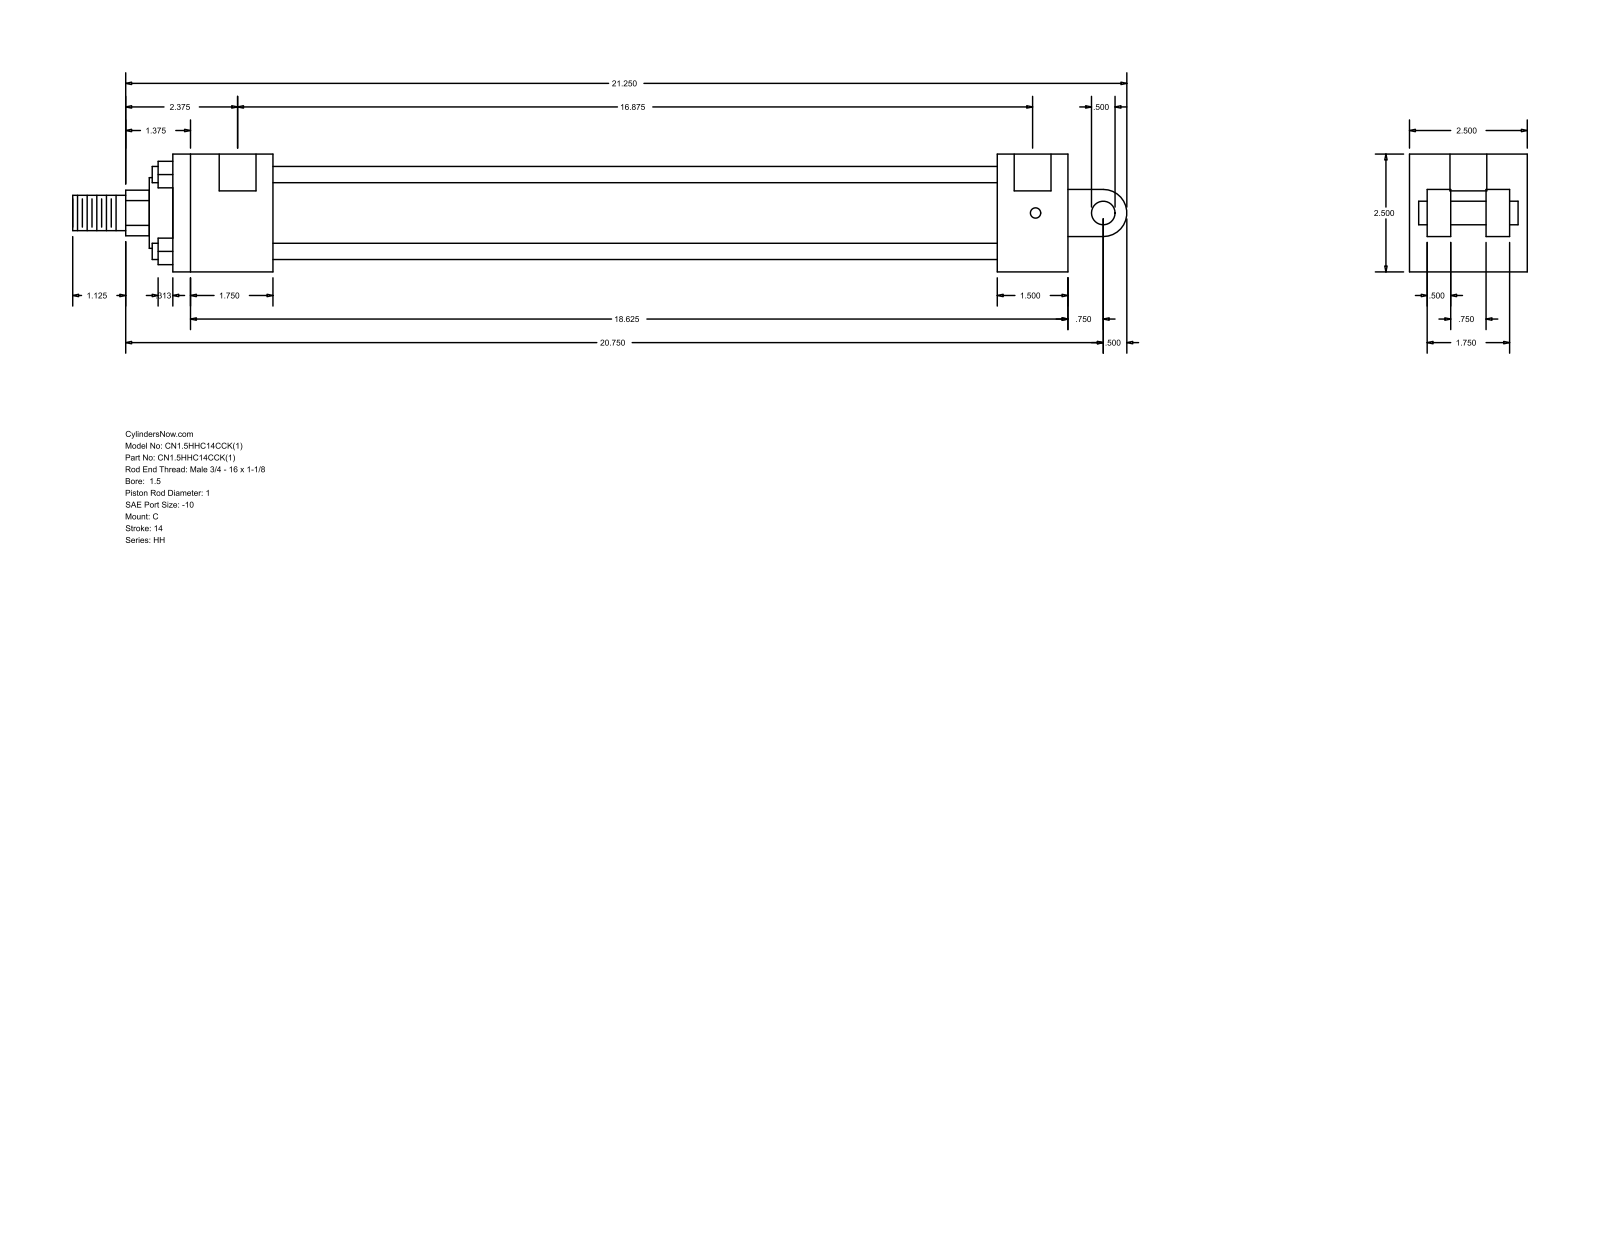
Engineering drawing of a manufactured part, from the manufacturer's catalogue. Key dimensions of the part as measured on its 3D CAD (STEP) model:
Part name (STEP PRODUCT): HH_C__0150_1
STEP written by: GSSL Pune (CONFIG_CONTROL_DESIGN)
Units: millimetres
Bodies: 0 solids, 99 faces (70 planar, 29 cylindrical, 0 other)
Overall size (bounding box): 568.33 × 63.5 × 63.5
Round holes (diameter × count): ⌀5.56 ×4, ⌀19.84 ×2
Round bosses / shafts (diameter × count): ⌀8.76 ×4, ⌀44.45 ×1, ⌀38.1 ×1, ⌀25.4 ×1, ⌀19.05 ×1, ⌀12.7 ×1
Partial cylindrical surfaces — rounded edges, fillets, slot ends (radius × count): R12.29 ×1, R12.7 ×1
Main face-to-face distances: 63.5, 53.98, 38.1, 390.52, 428.62, 444.5, 482.6, 12.7, 9.52, 22.22
Hole centre spacings: 1.59, 430.21, 431.8, 428.62
